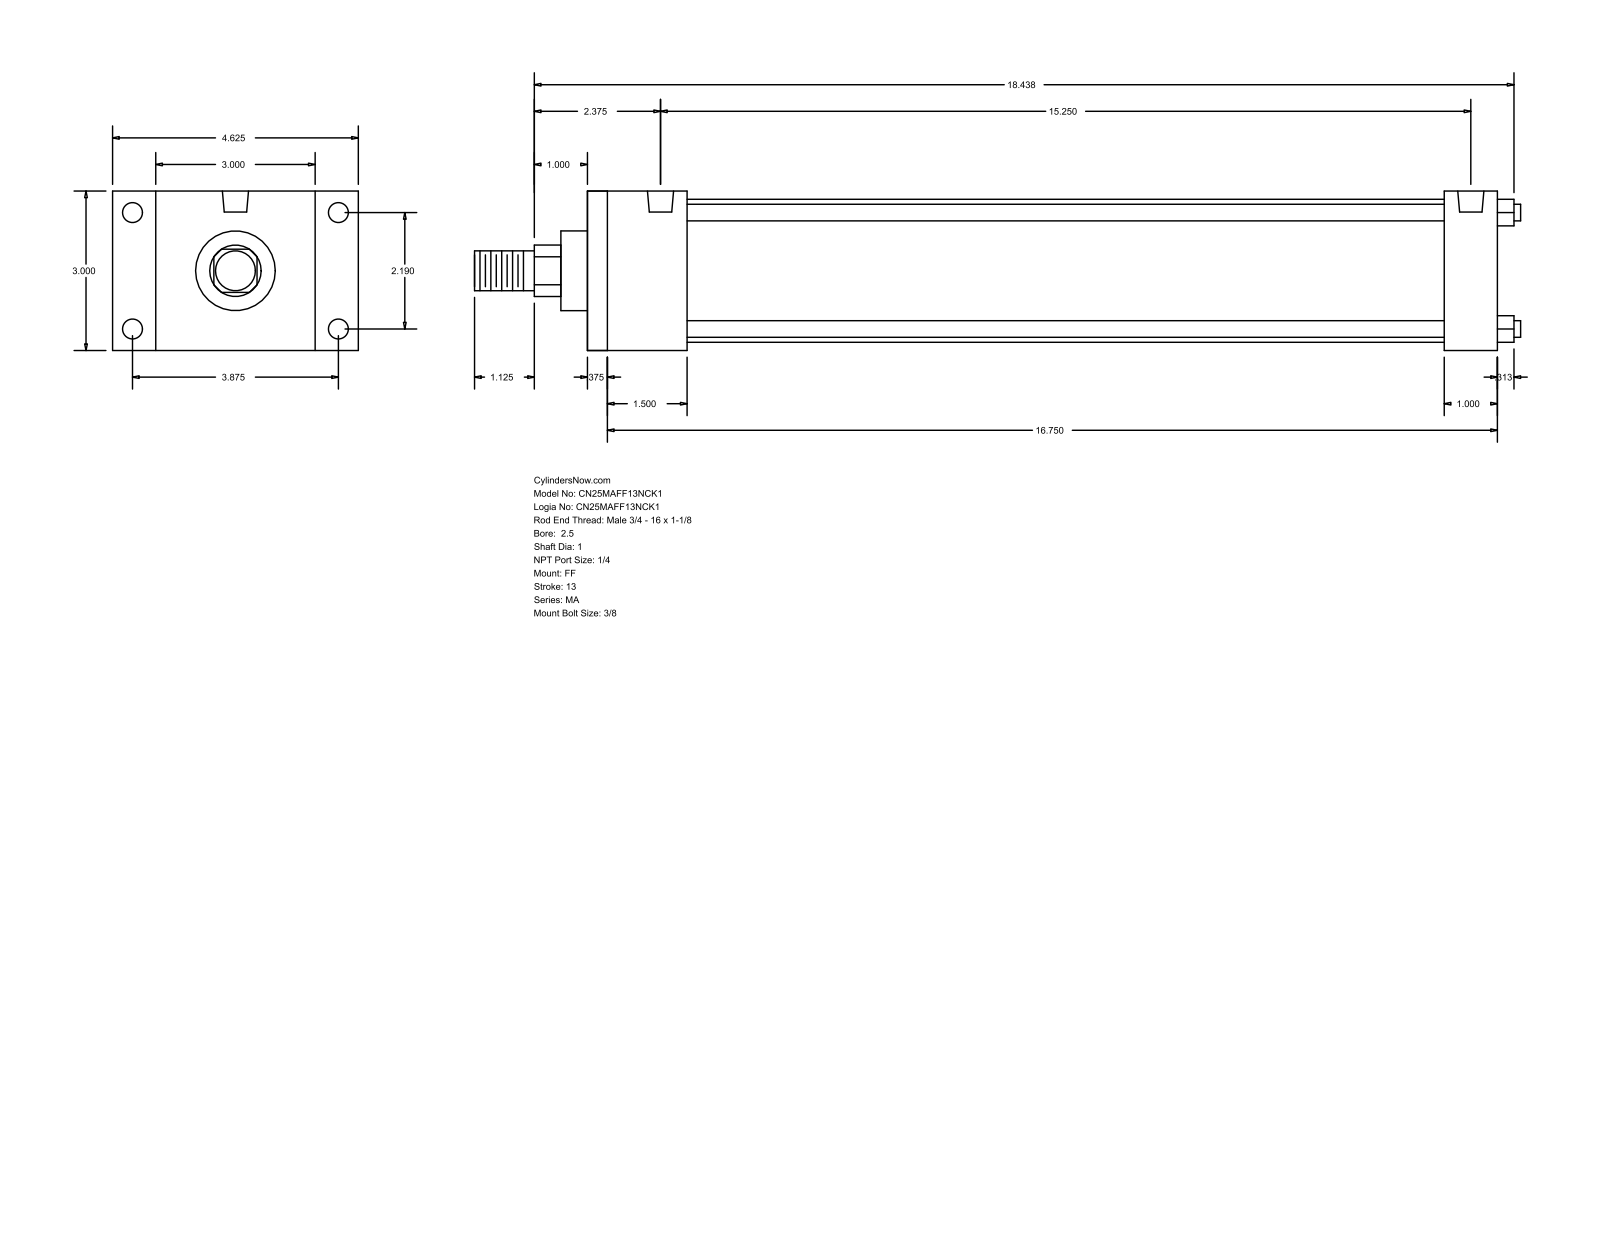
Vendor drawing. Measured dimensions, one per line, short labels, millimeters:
name: MA_FF__0250_1
written by: GSSL Pune (CONFIG_CONTROL_DESIGN)
unit: mm
bodies: 0 solids, 92 faces (64 planar, 28 cylindrical, 0 other)
size: 500.06 × 117.47 × 76.2
holes: 4× ⌀7.94, 4× ⌀9.53, 2× ⌀12.49
bosses: 4× ⌀7.94, 1× ⌀68.33, 1× ⌀38.1, 1× ⌀25.4, 1× ⌀19.05
rounds: 1× R12.29
face distances: 76.2, 434.98, 9.52, 425.46, 25.4, 47.63, 409.58, 38.11, 400.06, 361.95
hole spacings: 55.62, 98.42, 113.05, 387.35
